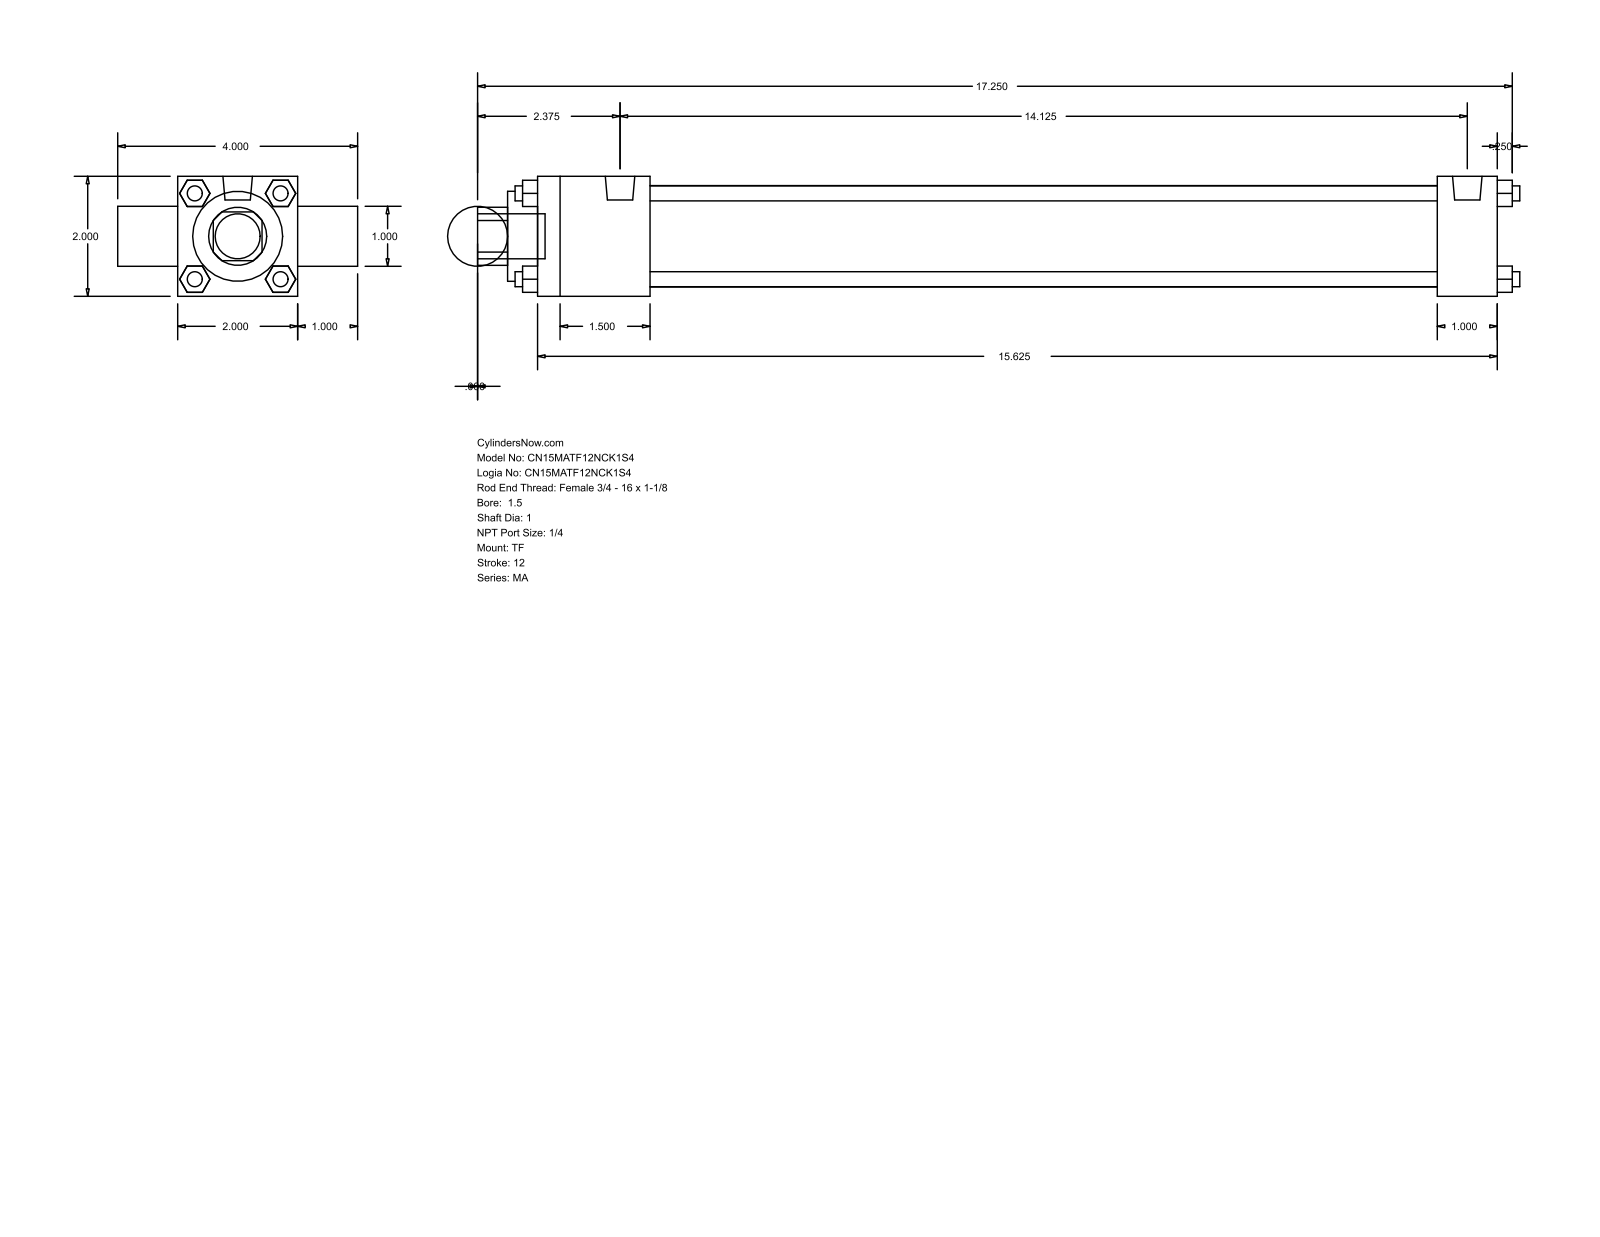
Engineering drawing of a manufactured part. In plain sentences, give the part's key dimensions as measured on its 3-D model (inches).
The part is named "MA_TF__0150_1". Its 3-D file was written by "GSSL Pune (CONFIG_CONTROL_DESIGN)". It is 0 solids with 120 faces: 92 planar, 28 cylindrical and 0 other. Overall it measures 17.375 by 4 by 2 inches. Round holes: 2 of diameter 1, 1 of diameter 1.5, 1 of diameter 1.69. Round bosses or shafts: 4 of diameter 0.25, 3 of diameter 0.313, 2 of diameter 0.492, 1 of diameter 0.75. Partial cylindrical surfaces (rounded edges, fillets, slot ends): 1 of radius 0.484. The main face-to-face distances are 2, 1, 16, 3, 0.25, 1.875, 15, 13.125, 14.125, 16.5.
